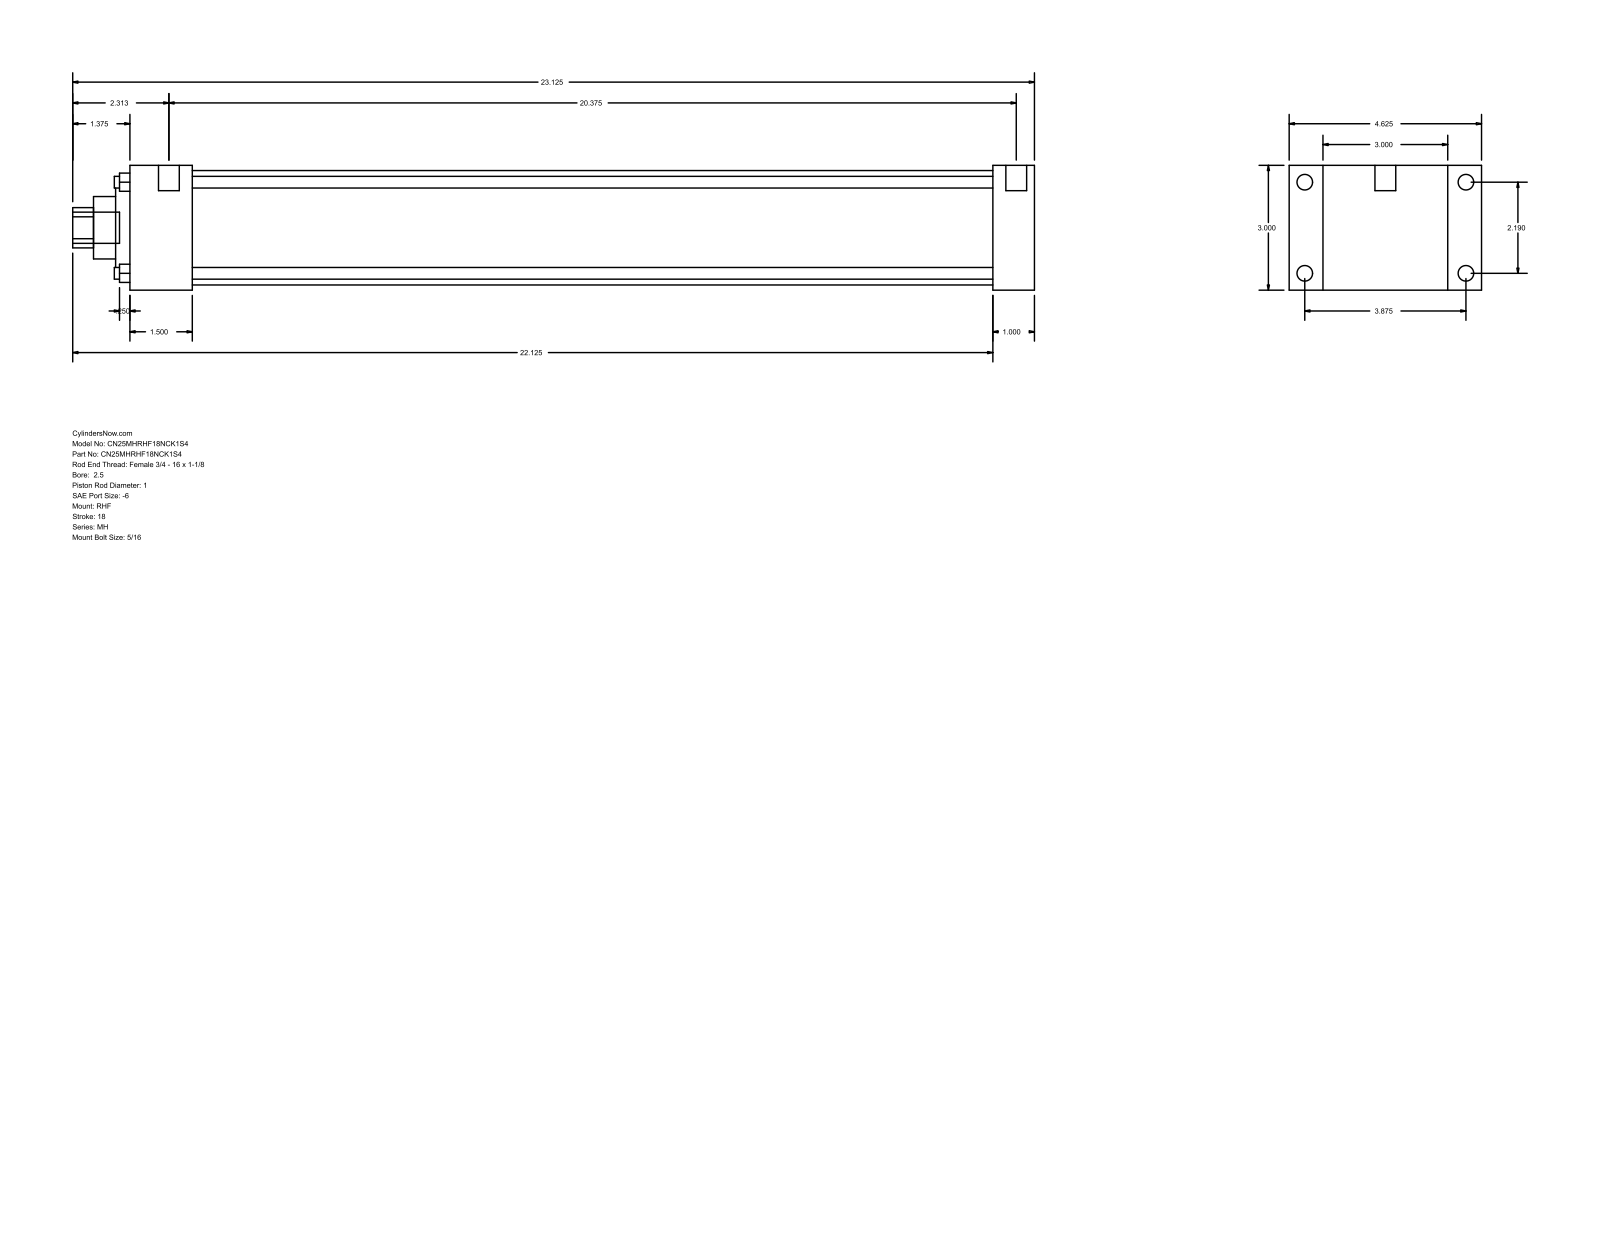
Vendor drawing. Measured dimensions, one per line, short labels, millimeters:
name: MH_RHF__0250_1
written by: GSSL Pune (CONFIG_CONTROL_DESIGN)
unit: mm
bodies: 0 solids, 90 faces (61 planar, 29 cylindrical, 0 other)
size: 587.38 × 117.47 × 76.2
holes: 4× ⌀7.14, 1× ⌀25.4, 1× ⌀38.1, 1× ⌀60.33, 1× ⌀69.85
bosses: 4× ⌀9.53, 4× ⌀5.56, 2× ⌀12.7, 1× ⌀19.05
rounds: 1× R12.29
face distances: 76.2, 25.4, 20.64, 96.84, 527.06, 552.46, 117.48, 38.11, 488.95, 514.35
hole spacings: 39.33, 55.62, 78.66
